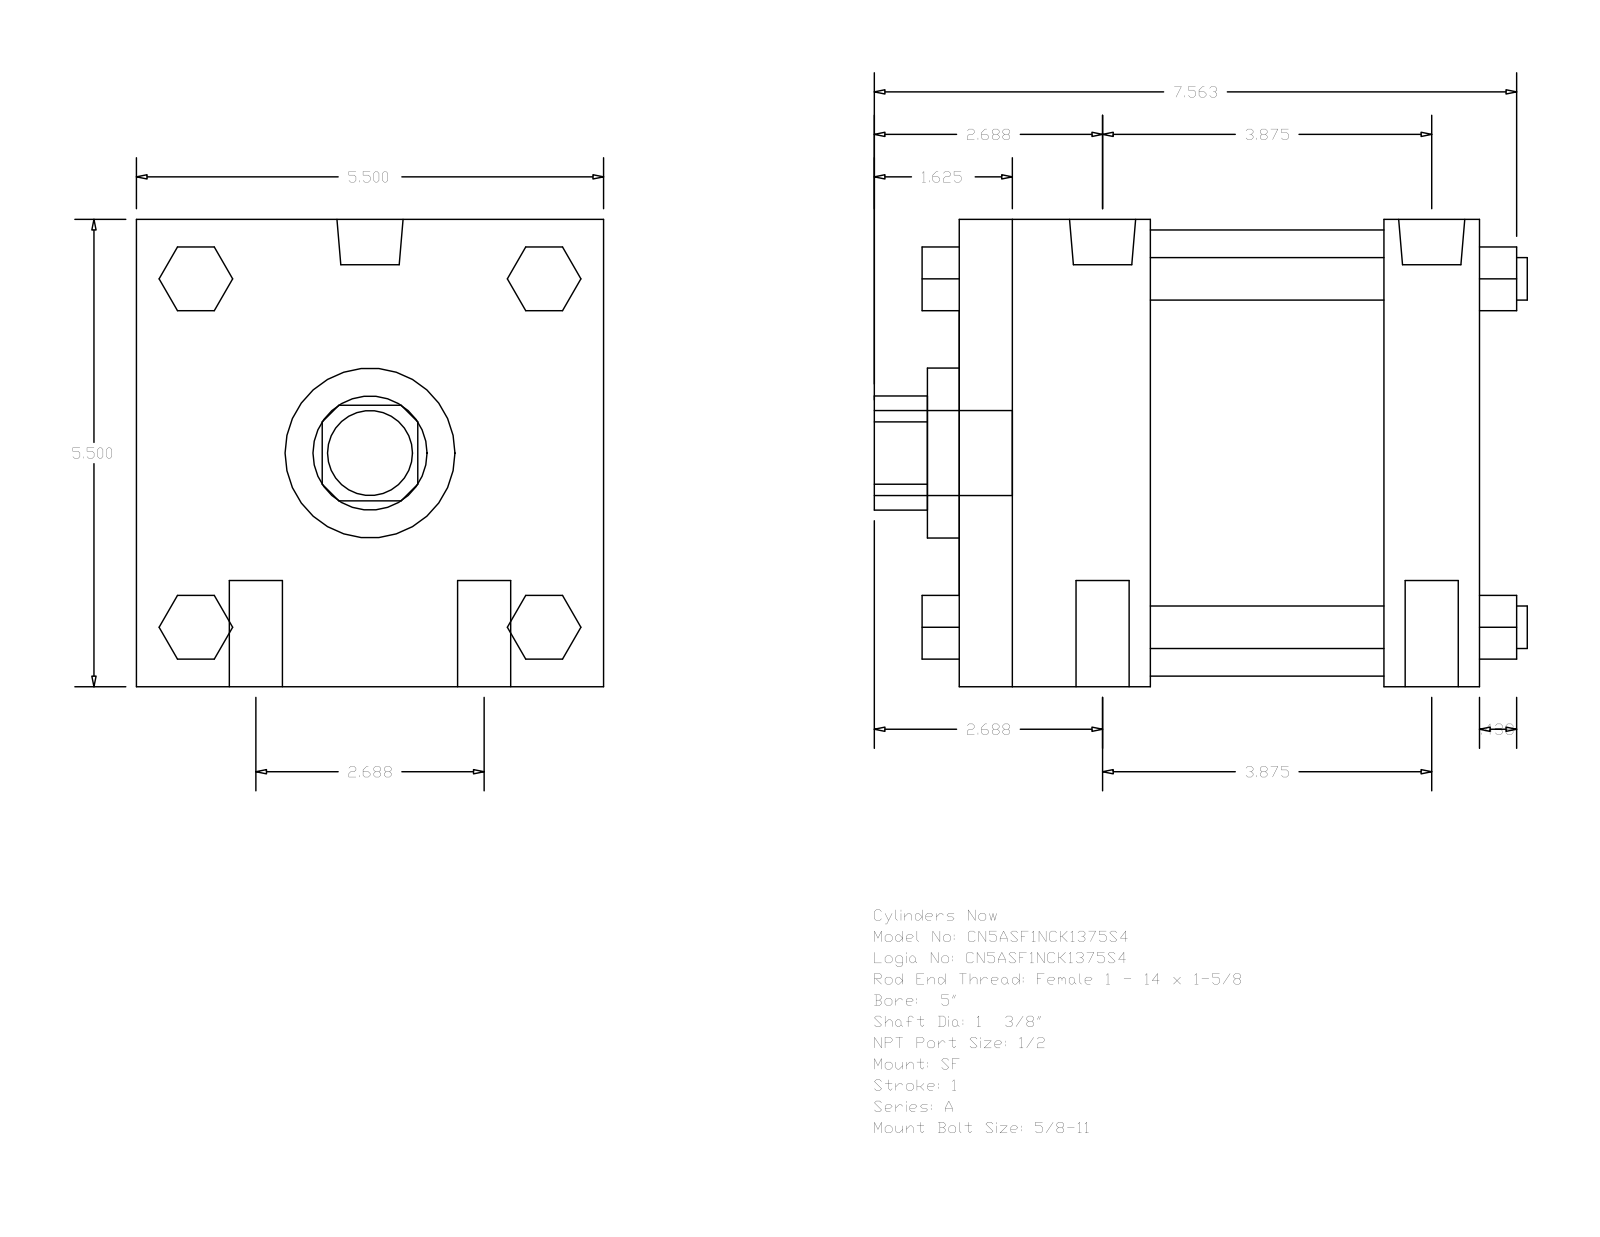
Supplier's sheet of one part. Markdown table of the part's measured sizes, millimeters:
| quantity | value |
| --- | --- |
| part name | A_SF__0500_1.375 |
| STEP written by | GSSL Pune (CONFIG_CONTROL_DESIGN) |
| units | millimeters |
| bodies | 0 solids, 124 faces (94 planar, 30 cylindrical, 0 other) |
| overall size | 195.26 × 139.7 × 139.7 |
| round holes (diameter × count) | 34.92 × 1, 50.8 × 1, 133.35 × 1 |
| round bosses / shafts (diameter × count) | 15.88 × 4, 12.7 × 4, 19.77 × 2, 8.73 × 2, 25.4 × 1 |
| partial cylindrical surfaces (radius × count) | 17.06 × 1 |
| main face-to-face distances | 139.7, 155.57, 127, 28.57, 69.85, 57.15, 98.42, 19.05, 52.07, 90.18 |
